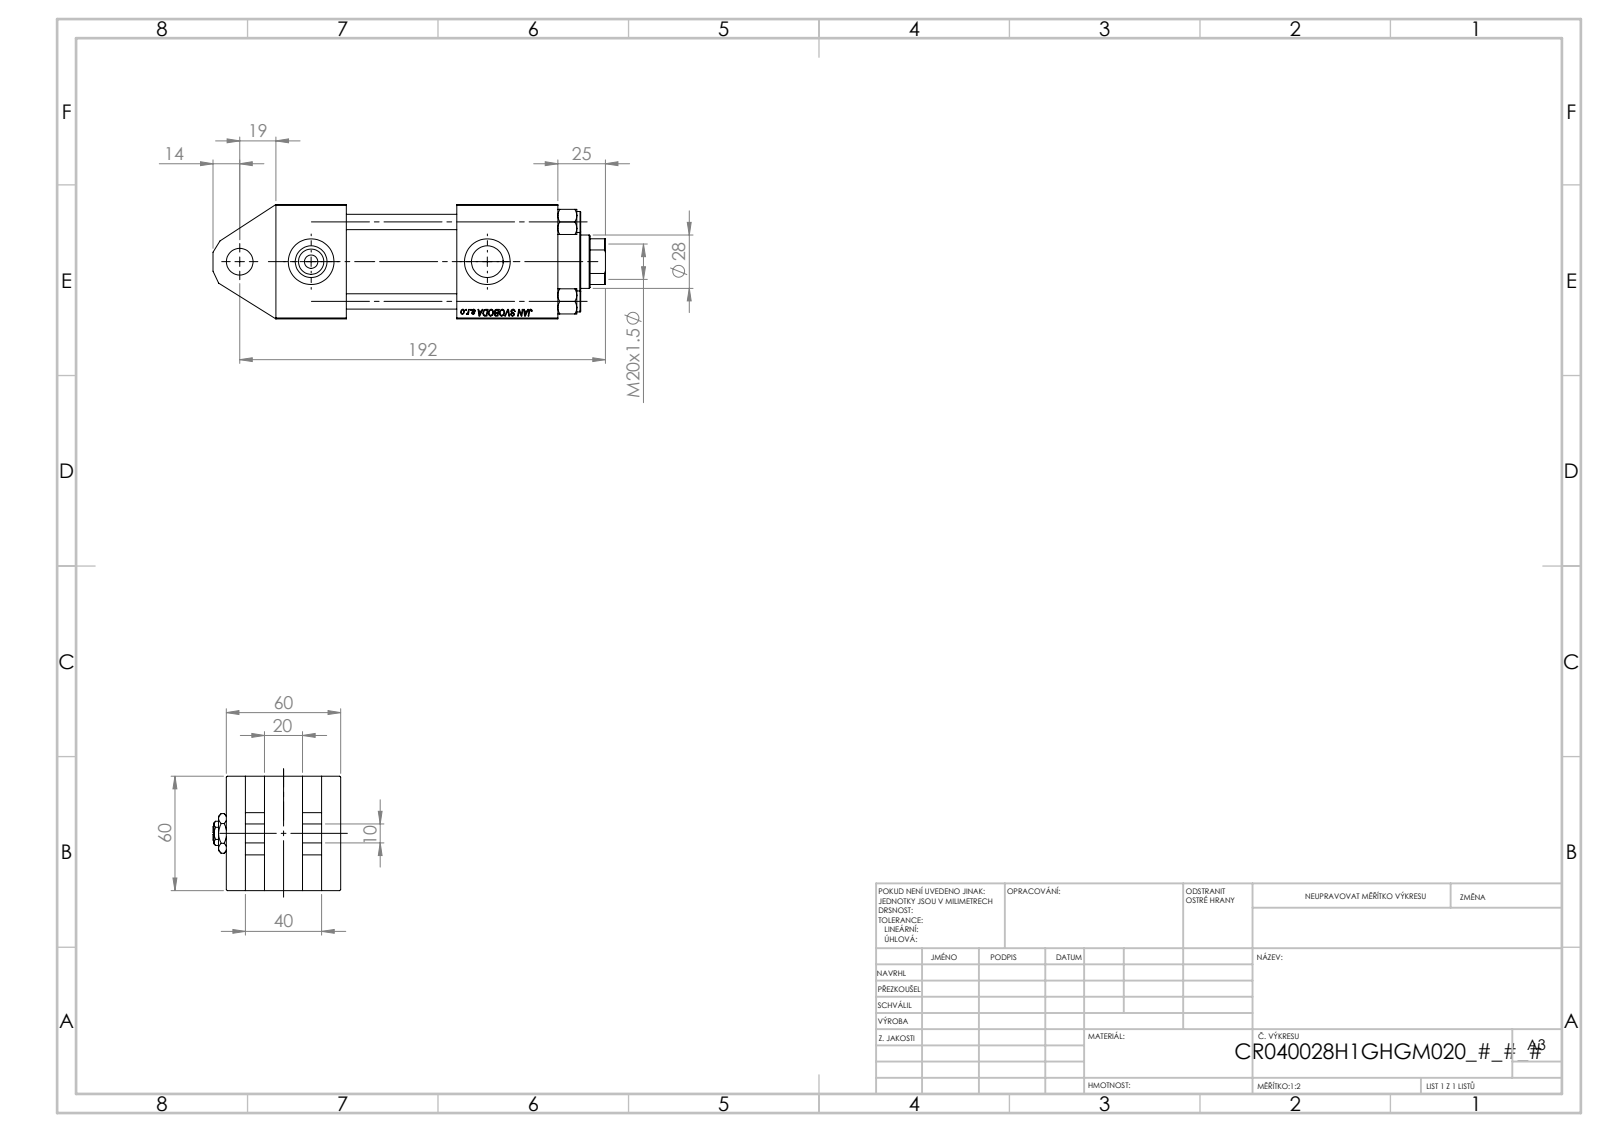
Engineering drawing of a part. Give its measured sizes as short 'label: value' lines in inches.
name: V215_VC_A; Zatka_pro_OIL_PORT; V215CR_VCP_H; V215CR_H_Body (+2 more)
written by: SolidWorks 2019 (CONFIG_CONTROL_DESIGN)
unit: in
bodies: 12 solids, 1184 faces (542 planar, 90 cylindrical, 552 other)
size: 8.11 × 2.638 × 2.362
volume: 27.37 in³; area: 186 in²
holes: 4× ⌀0.315, 2× ⌀0.276, 2× ⌀0.656, 2× ⌀0.945, 1× ⌀0.551, 1× ⌀0.728, 1× ⌀1.102, 1× ⌀1.22, 1× ⌀1.575, 1× ⌀1.772
bosses: 4× ⌀0.433, 1× ⌀1.811, 1× ⌀1.654
rounds: 2× R0.049, 1× R0.531
face distances: 2.362, 0.394, 0.787, 1.575, 2.087, 1.457, 2.283, 1.969, 1.181, 3.74
hole spacings: 1.161, 1.642, 2.322, 1.476, 3.642, 5.118
